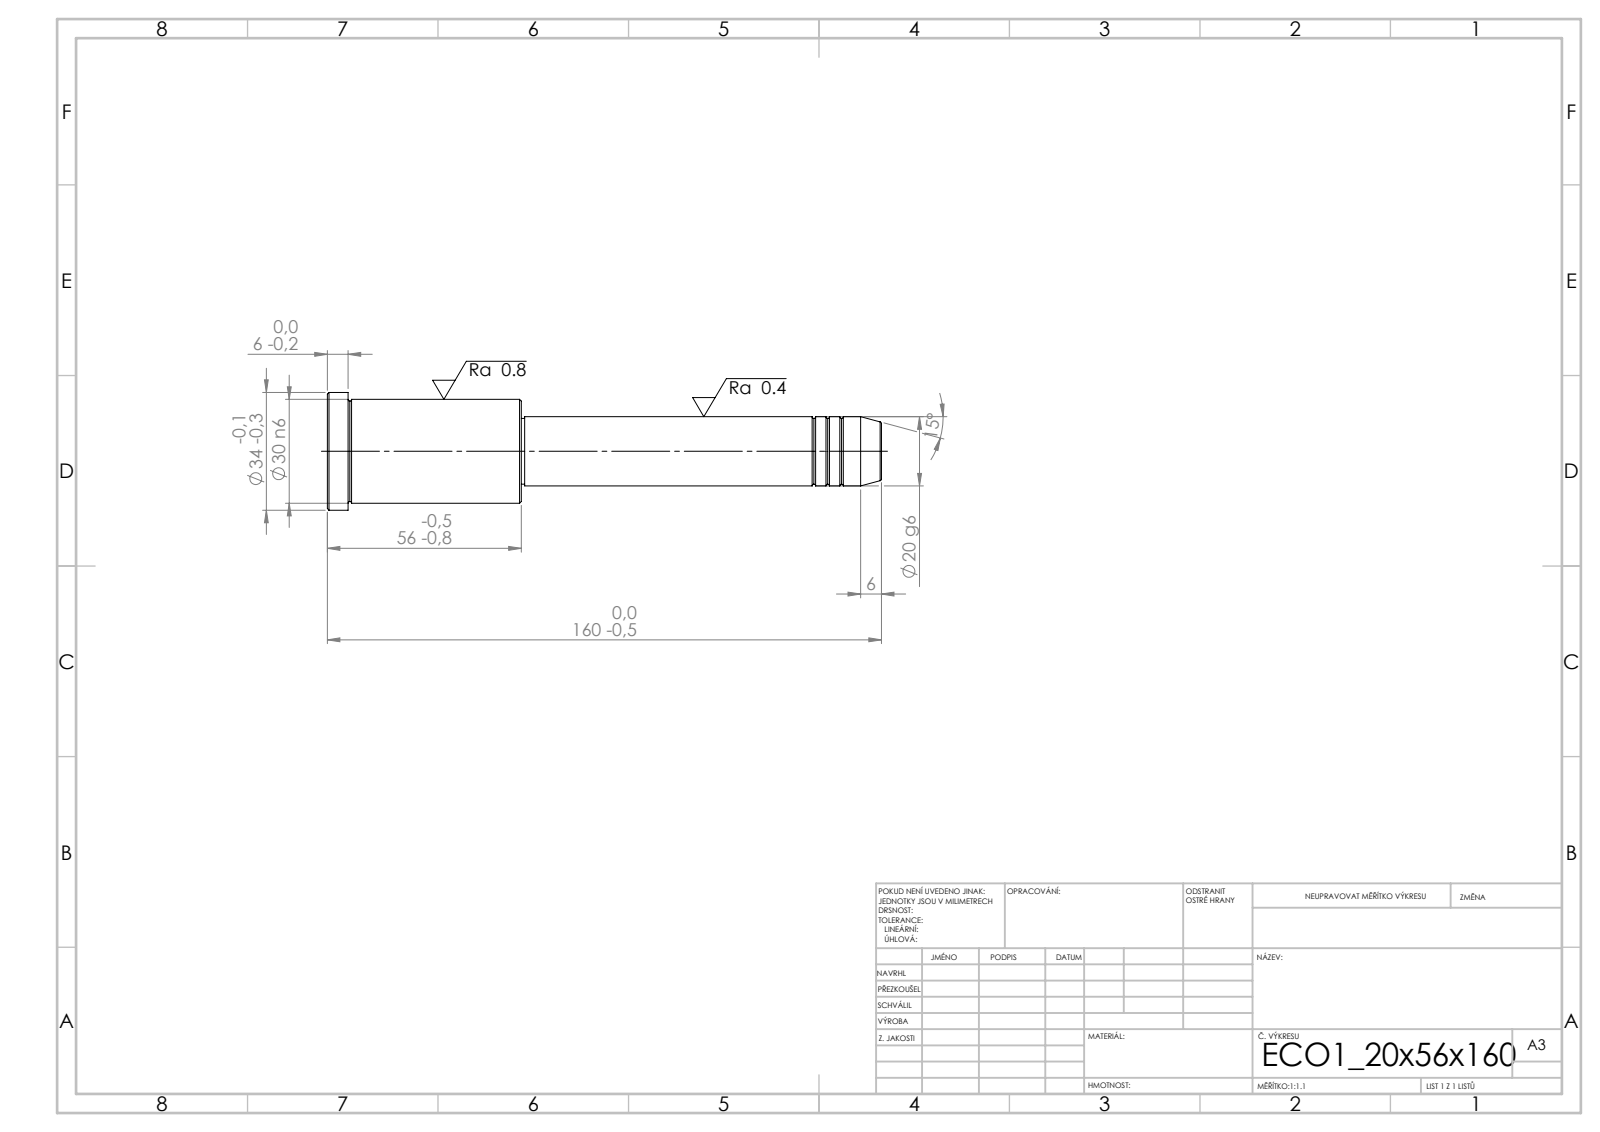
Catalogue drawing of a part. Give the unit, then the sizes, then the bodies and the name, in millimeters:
Units: millimetres
Overall size (bounding box): 160 × 34 × 34
Round bosses / shafts (diameter × count): ⌀34 ×1, ⌀30 ×1, ⌀20 ×1, ⌀19 ×1
Main face-to-face distances: 56, 104, 160, 154, 50, 6, 103, 1, 51, 57
Volume: 73 010 mm³ · Surface area: 13 734 mm²
Bodies: 1 solid, 43 faces (5 planar, 14 cylindrical, 24 other)
STEP written by: SolidWorks 2019 (CONFIG_CONTROL_DESIGN)
